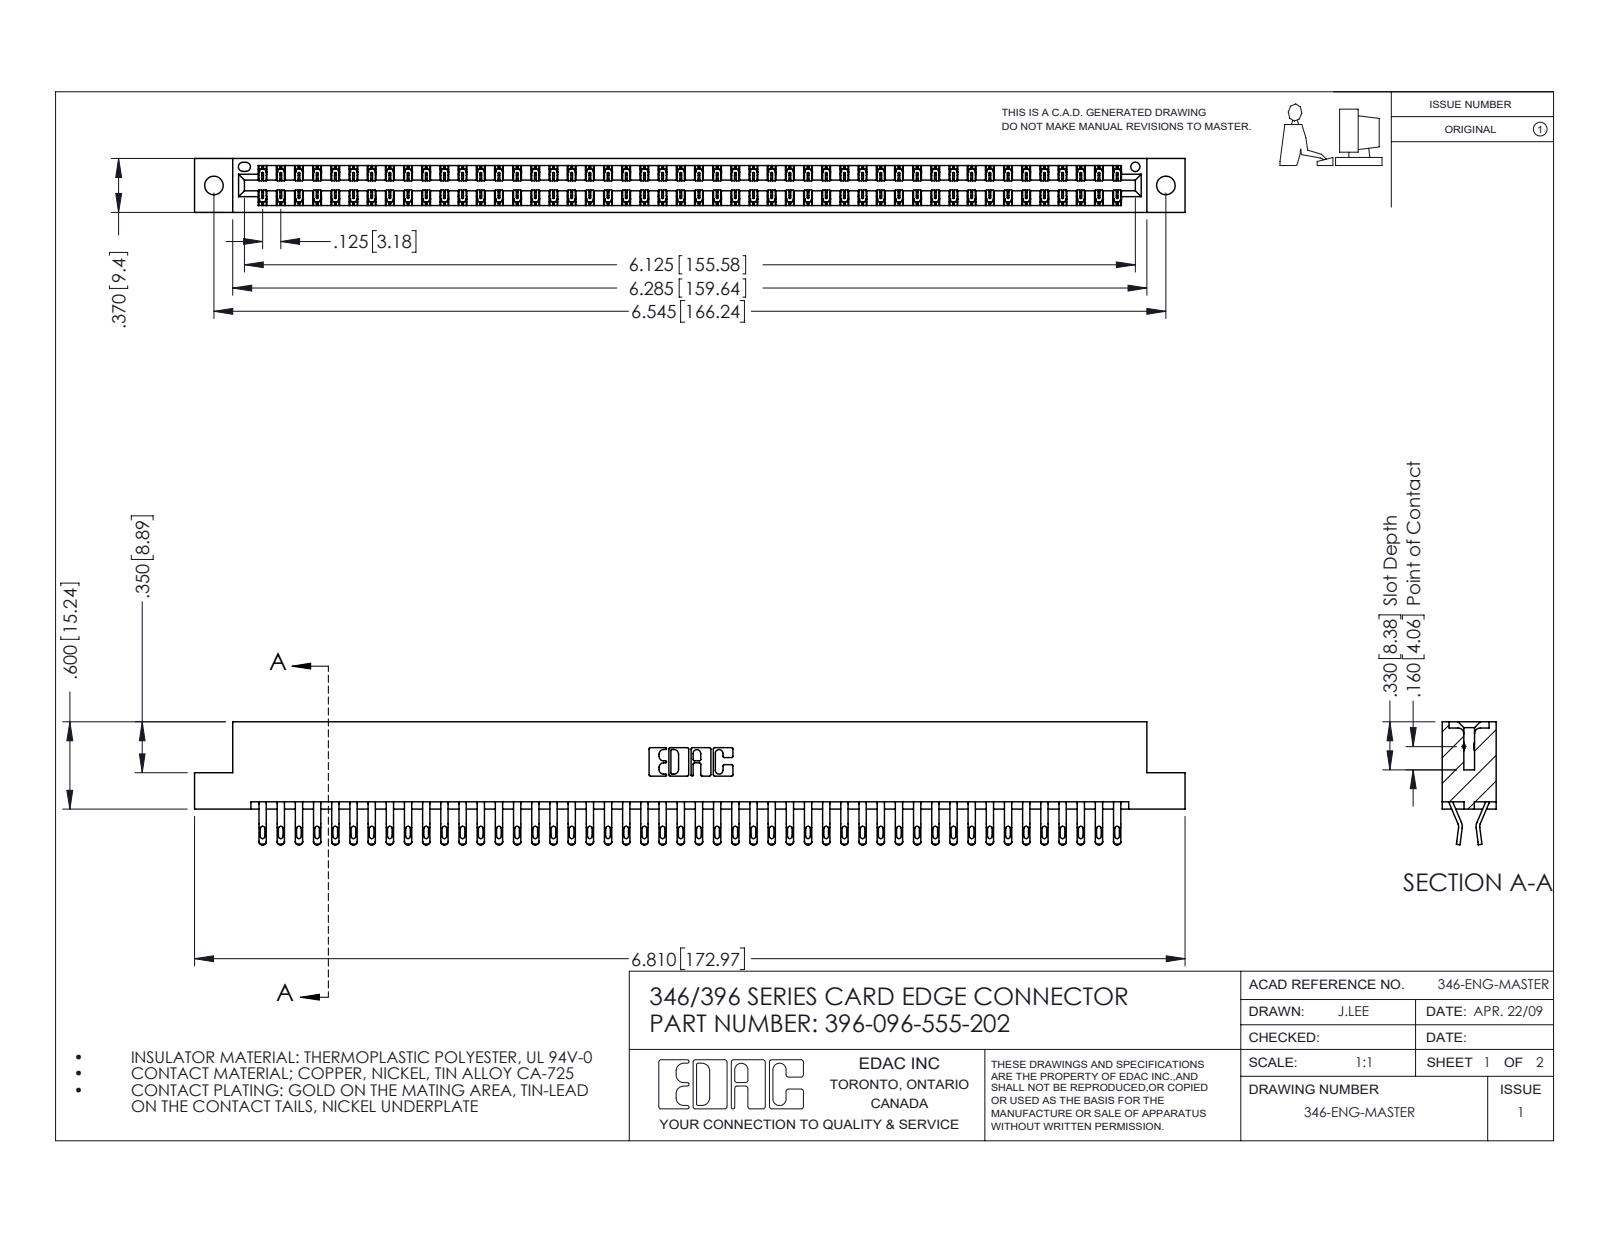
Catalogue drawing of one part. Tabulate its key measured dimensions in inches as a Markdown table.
| quantity | value |
| --- | --- |
| part name | 346 Part_Flush Mounting Lugs - 0.128 Dia; 396-096-555-202; 345-292-001_555 Tail |
| STEP written by | SolidWorks 2016 (CONFIG_CONTROL_DESIGN) |
| units | inches |
| bodies | 97 solids, 5690 faces (3244 planar, 2446 cylindrical, 0 other) |
| overall size | 6.81 × 0.845 × 0.37 |
| volume | 1.047 in³ |
| surface area | 37.82 in² |
| round holes (diameter × count) | 0.128 × 2, 0.064 × 1 |
| partial cylindrical surfaces (radius × count) | 0.016 × 192, 0.02 × 192, 0.006 × 144, 0.01 × 22, 0.007 × 6, 0.031 × 6, 0.026 × 3, 0.01 × 2 |
| main face-to-face distances | 0.048, 0.322, 0.37, 0.25, 0.025, 0.072, 0.298, 0.275, 0.148, 0.222 |
| hole center spacings | 0.246, 6.336, 6.545 |
